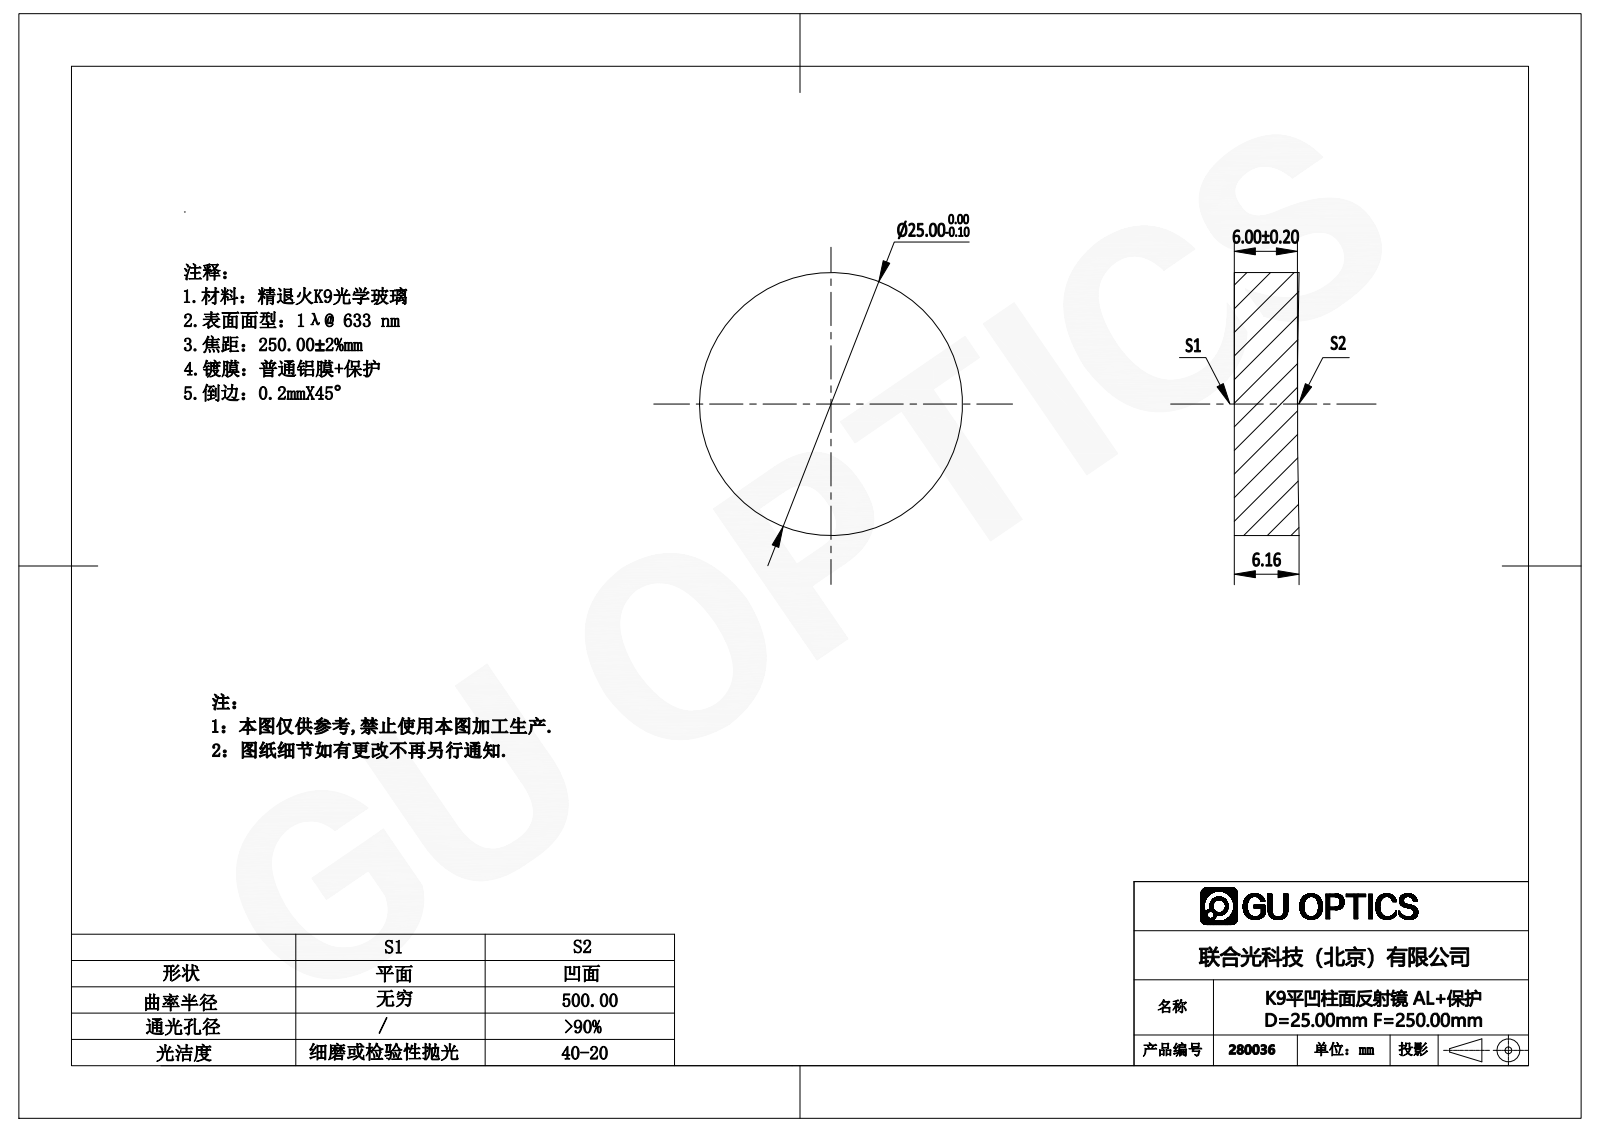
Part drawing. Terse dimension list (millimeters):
name: 280014
written by: SolidWorks 2020 (CONFIG_CONTROL_DESIGN)
unit: mm
bodies: 1 solid, 3 faces (1 planar, 2 cylindrical, 0 other)
size: 25 × 25 × 6.16
volume: 2 964 mm³; area: 1 459 mm²
bosses: 1× ⌀25
rounds: 1× R500
